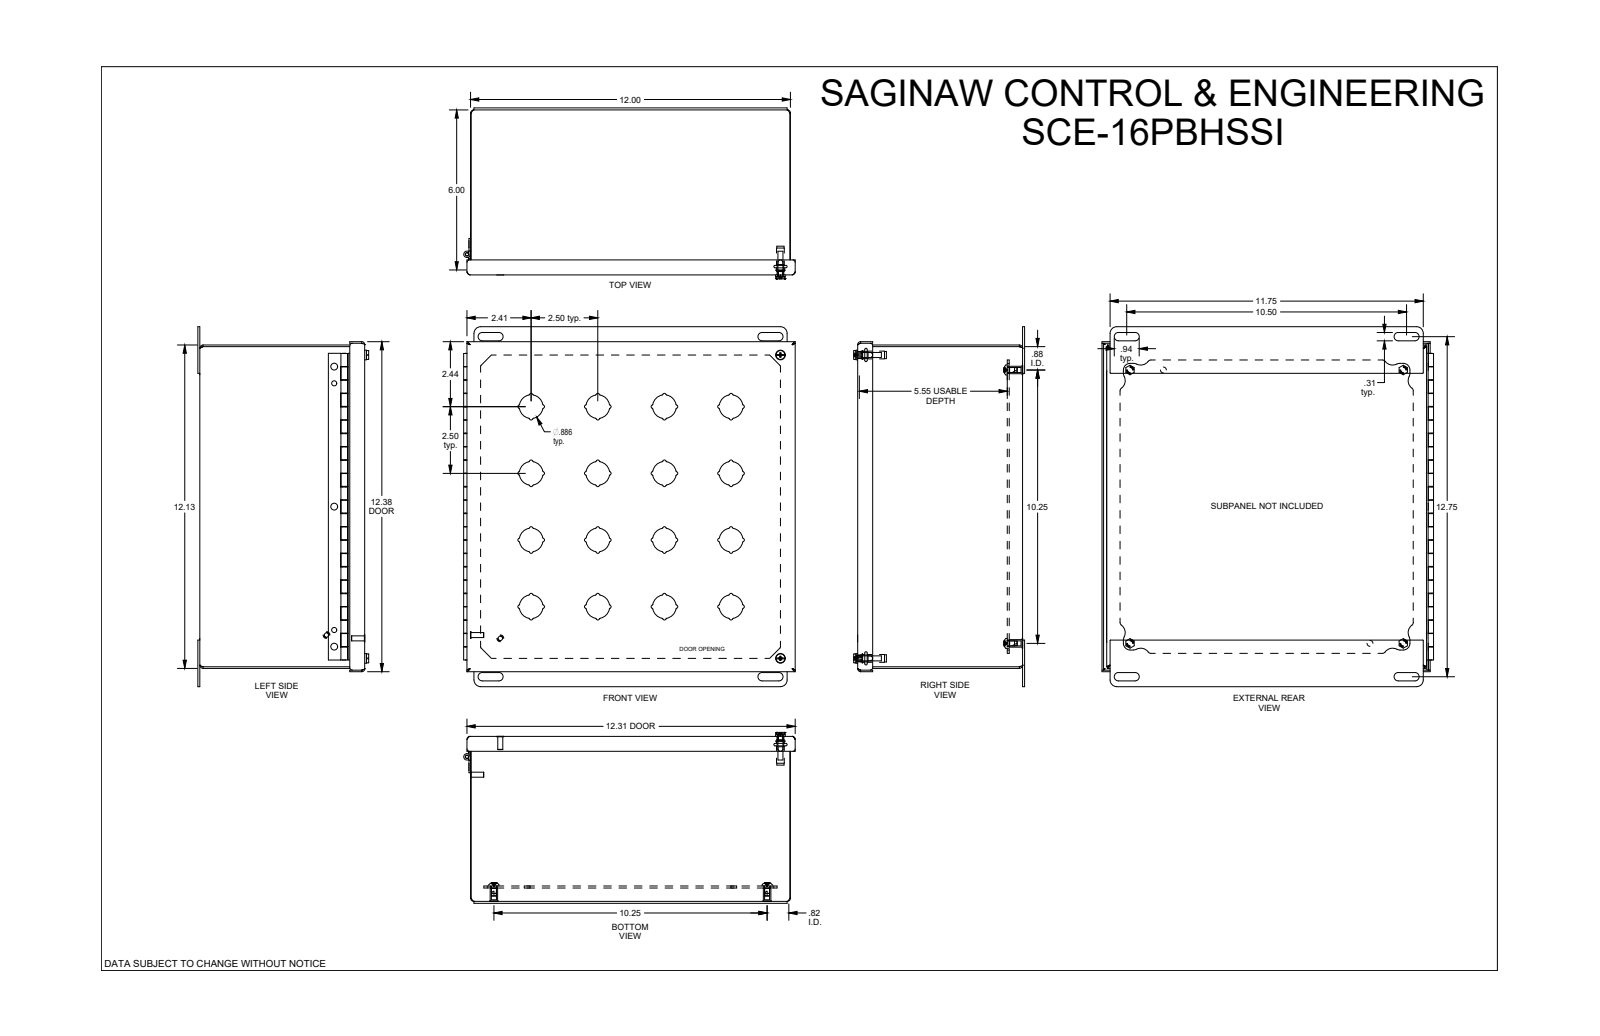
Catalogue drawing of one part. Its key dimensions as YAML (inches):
part_name: "SCE-16PBHI"
step_written_by: "SolidWorks 2021 (AUTOMOTIVE_DESIGN)"
units: inches
bodies: {solids: 7, faces: 1118, planar: 408, cylindrical: 558, other: 152}
overall_size: [13.5, 12.438, 6.323]
volume: 53.22
surface_area: 1604
round_holes:
  - {diameter: 0.19, count: 9}
  - {diameter: 0.25, count: 6}
  - {diameter: 0.281, count: 4}
  - {diameter: 0.317, count: 4}
  - {diameter: 0.126, count: 2}
  - {diameter: 0.193, count: 2}
  - {diameter: 0.218, count: 2}
  - {diameter: 0.22, count: 2}
  - {diameter: 0.266, count: 2}
round_bosses_or_shafts:
  - {diameter: 0.188, count: 5}
  - {diameter: 0.437, count: 4}
  - {diameter: 0.28, count: 4}
  - {diameter: 0.256, count: 4}
  - {diameter: 0.362, count: 2}
  - {diameter: 0.292, count: 2}
  - {diameter: 0.27, count: 2}
  - {diameter: 0.26, count: 2}
partial_cylinders:
  - {radius: 0.04, count: 128}
  - {radius: 0.062, count: 64}
  - {radius: 0.06, count: 20}
  - {radius: 0.01, count: 18}
  - {radius: 0.25, count: 16}
  - {radius: 0.443, count: 16}
  - {radius: 0.063, count: 8}
  - {radius: 0.125, count: 8}
face_to_face_distances: [0.06, 6.125, 12.064, 6.065, 11.94, 6.185, 0.075, 0.435, 0.51, 0.495]
hole_center_spacings: [10.25, 10.764, 15.246, 10.823, 0.752, 0.753, 10.765, 10.784]
